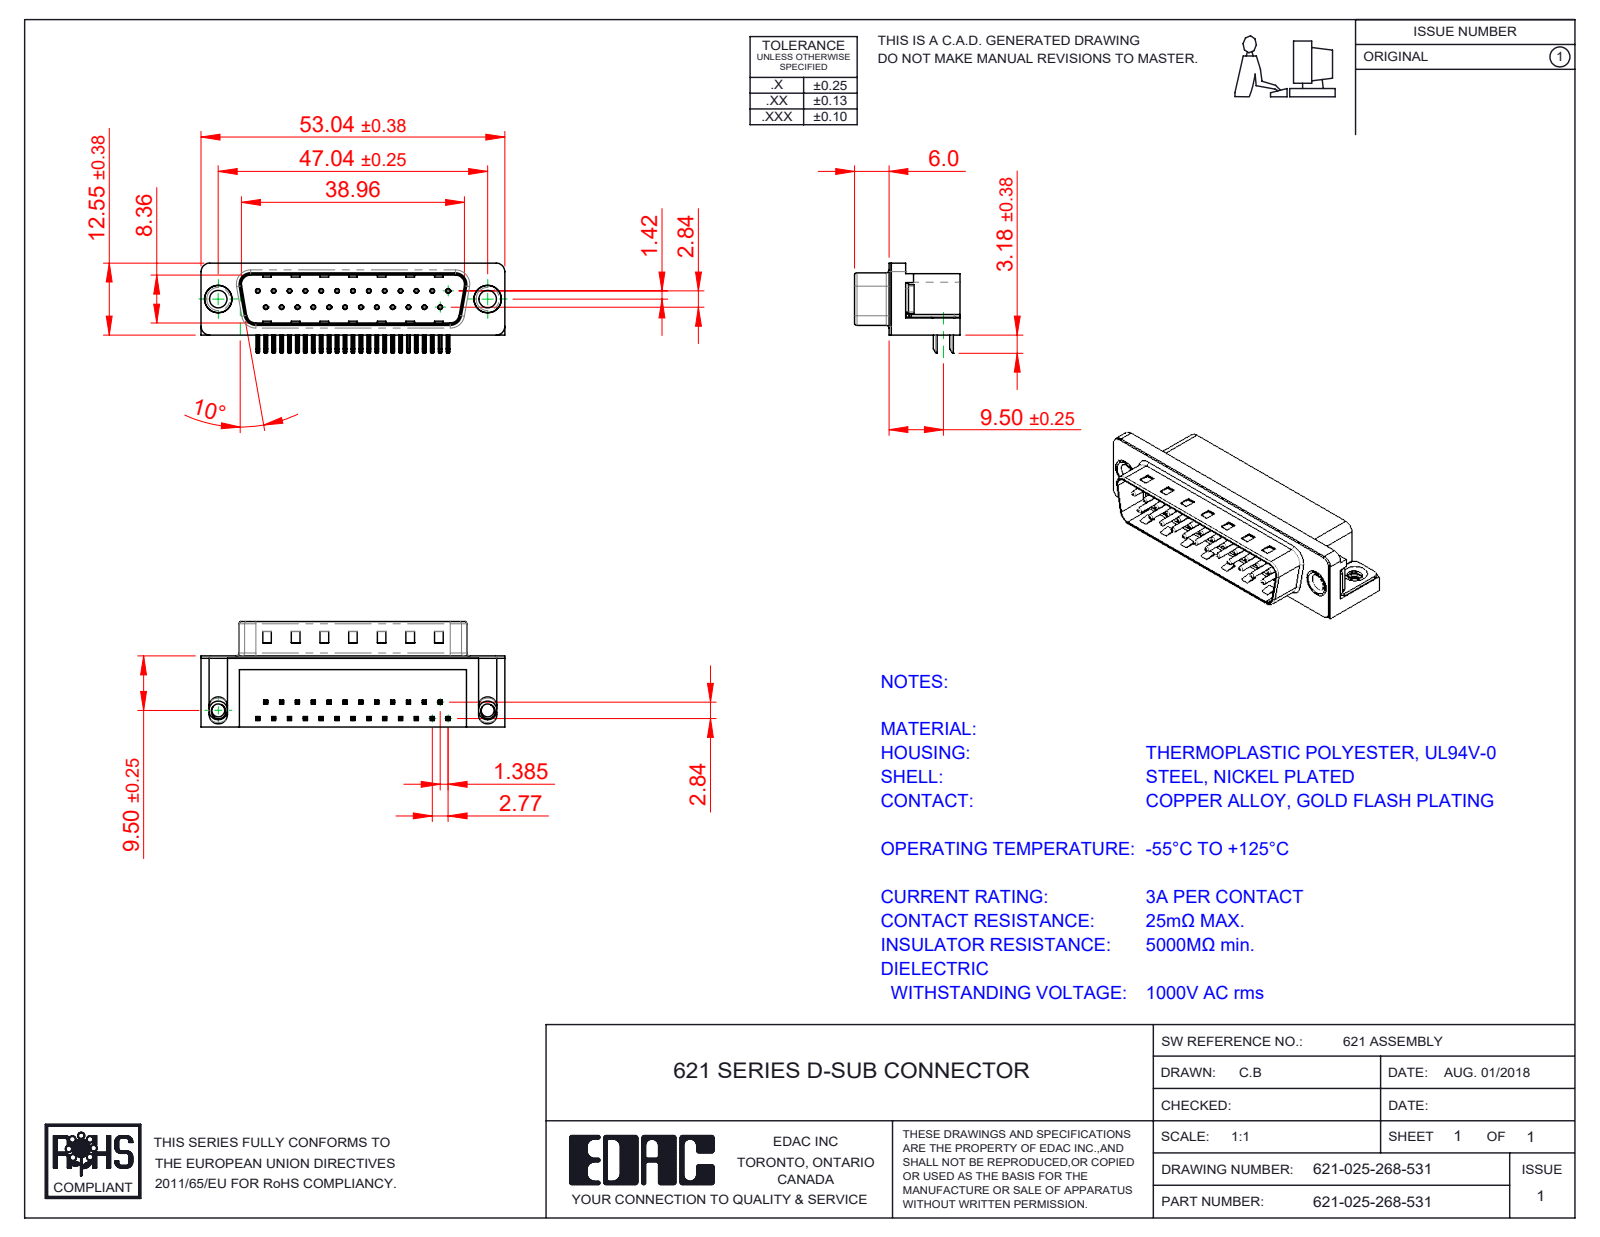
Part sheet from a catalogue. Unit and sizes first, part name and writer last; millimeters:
Units: millimetres
Overall size (bounding box): 53.04 × 18.4 × 16.25
Round holes (diameter × count): ⌀0.35 ×25, ⌀0.8 ×25, ⌀3.05 ×2, ⌀4 ×2, ⌀4.8 ×2, ⌀5 ×2
Round bosses / shafts (diameter × count): ⌀0.75 ×25, ⌀4.9 ×2, ⌀4.75 ×2, ⌀3.85 ×2
Partial cylindrical surfaces — rounded edges, fillets, slot ends (radius × count): R0.25 ×108, R0.12 ×50, R1 ×16, R0.5 ×14, R1.6 ×8, R1.5 ×7, R0.32 ×4, R0.9 ×4
Main face-to-face distances: 0.4, 12, 10.35, 2.1, 8.76, 10.46, 10.86, 1.7, 12.4, 9
Hole centre spacings: 3.16, 2.77, 5.54, 8.31, 11.08, 13.85, 16.62, 5.03
Volume: 6 335 mm³ · Surface area: 7 665 mm²
Bodies: 31 solids, 2263 faces (1437 planar, 649 cylindrical, 177 other)
Part name (STEP PRODUCT): 621 Shell_25 Socket; 621 Housing_25 Socket; 621 Contact Top; 621 Contact Bottom (+3 more)
STEP written by: SolidWorks 2016 (CONFIG_CONTROL_DESIGN)
